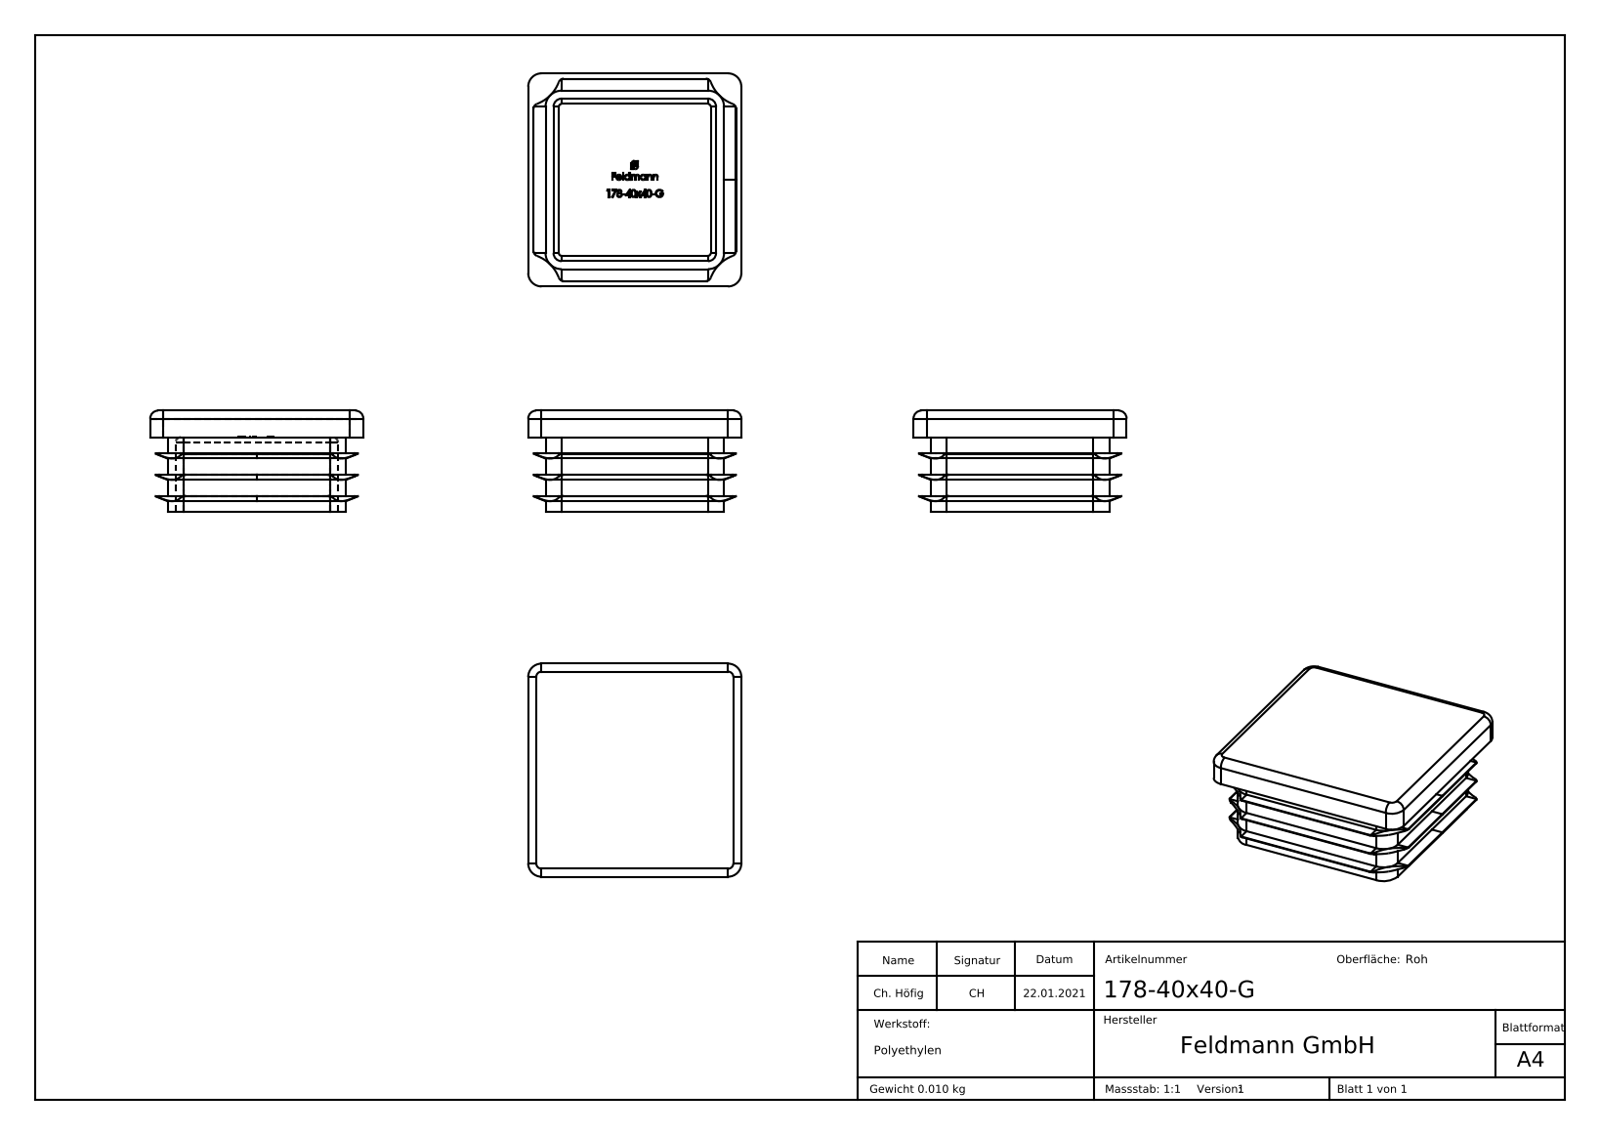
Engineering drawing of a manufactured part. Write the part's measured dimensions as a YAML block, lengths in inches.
part_name: "178-40x40-G"
step_written_by: "SolidWorks 2018 (CONFIG_CONTROL_DESIGN)"
units: inches
bodies: {solids: 1, faces: 474, planar: 247, cylindrical: 83, other: 144}
overall_size: [1.575, 1.575, 0.748]
volume: 0.669
surface_area: 13.37
partial_cylinders:
  - {radius: 0.039, count: 12}
  - {radius: 0.059, count: 8}
  - {radius: 0.098, count: 4}
  - {radius: 0.118, count: 4}
  - {radius: 0.276, count: 4}
face_to_face_distances: [0.197, 0.059, 1.26, 1.201, 1.319, 0.157, 0.315, 0.128, 0.187, 1.388]
